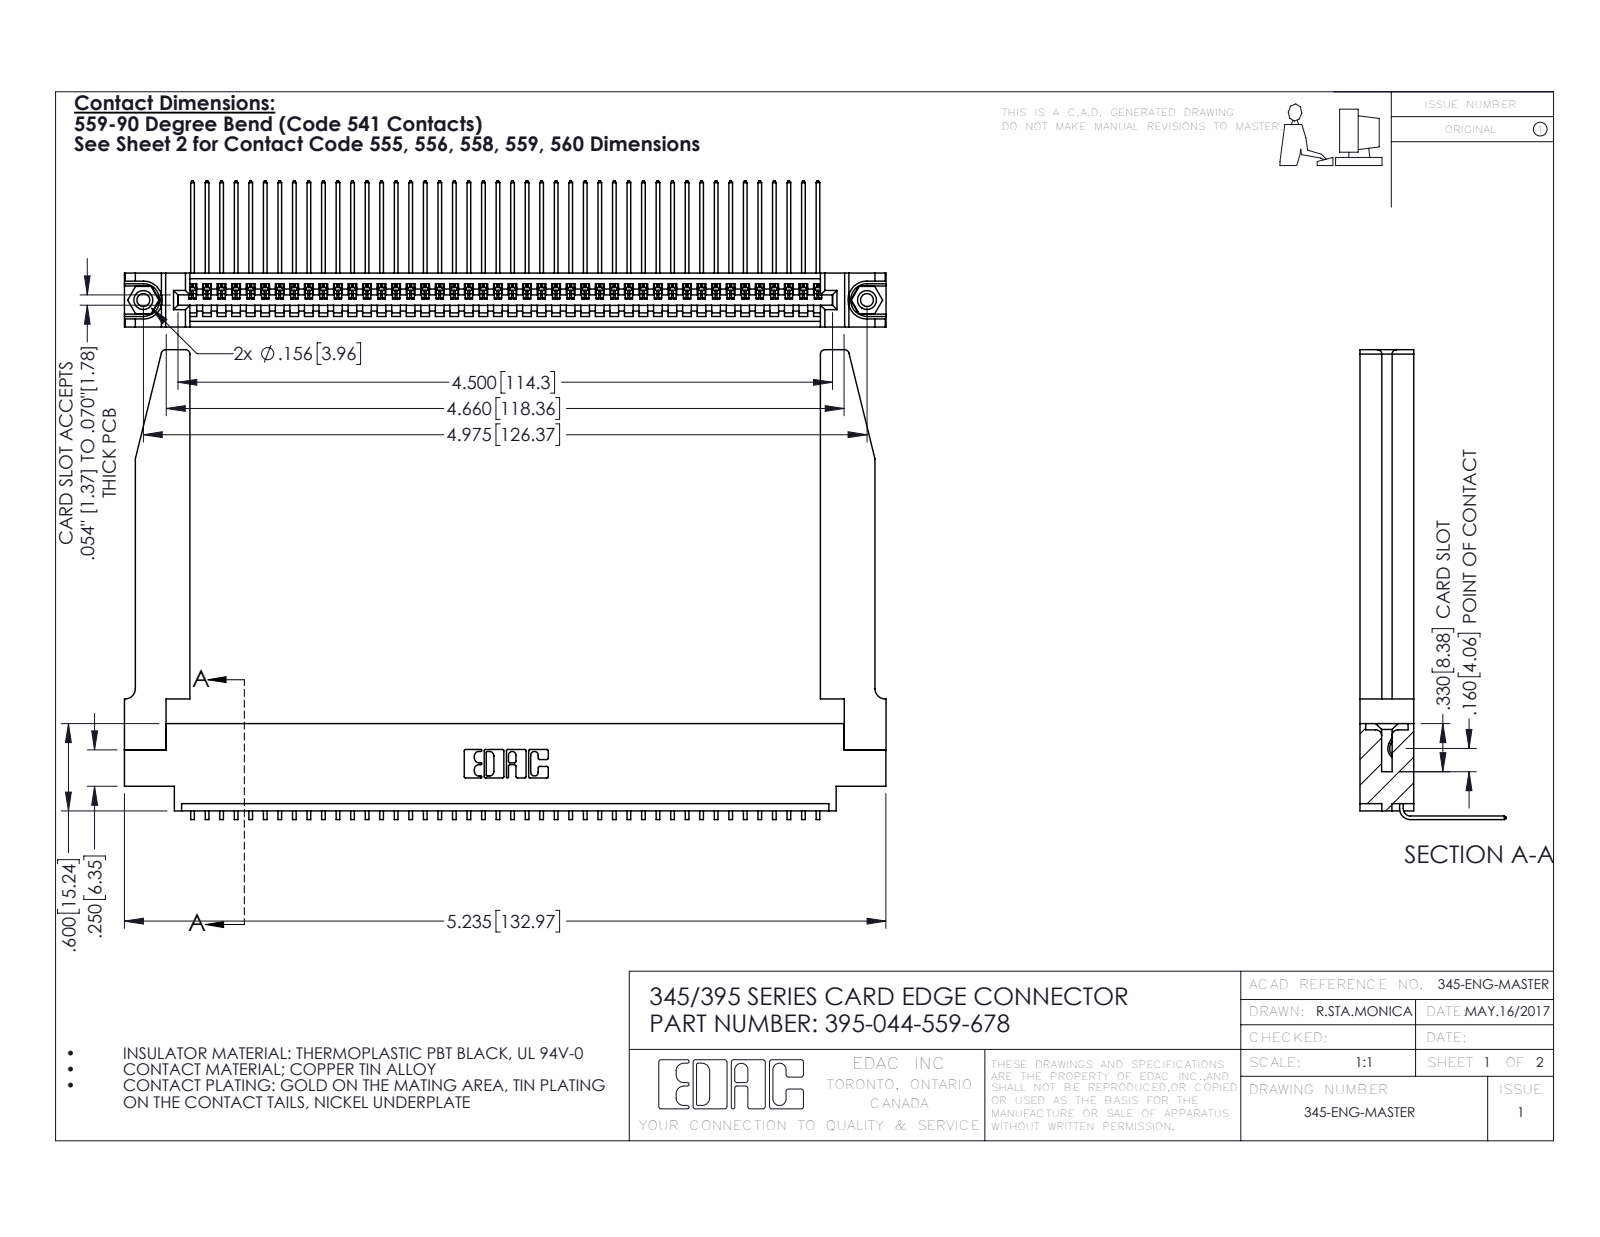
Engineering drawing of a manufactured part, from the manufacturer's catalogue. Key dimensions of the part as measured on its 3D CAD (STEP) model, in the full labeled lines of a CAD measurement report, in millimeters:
Part name (STEP PRODUCT): 345-250-001_345-250-001-102; 345 Part_0.170 Offset - 0.156 Dia-TH; 395-044-559-678; 345-292-001_558 559 Tail - 1 (+1 more)
STEP written by: SolidWorks 2016 (CONFIG_CONTROL_DESIGN)
Units: millimetres
Bodies: 49 solids, 3004 faces (2074 planar, 878 cylindrical, 52 other)
Overall size (bounding box): 133 × 82 × 25.5
Volume: 20 450 mm³ · Surface area: 24 720 mm²
Round holes (diameter × count): ⌀2.3 ×2, ⌀3.2 ×2, ⌀4 ×2, ⌀1.6 ×1
Round bosses / shafts (diameter × count): ⌀3.9 ×2
Partial cylindrical surfaces — rounded edges, fillets, slot ends (radius × count): R0.2 ×88, R0.3 ×22, R0.8 ×8, R0.2 ×6, R0.8 ×6, R0.7 ×3, R0.8 ×2, R1 ×2
Main face-to-face distances: 9.4, 1.8, 7.6, 5.1, 2.5, 6.9, 0.6, 5.7, 3.8, 3.8
Hole centre spacings: 6.9, 120.4, 126.4
